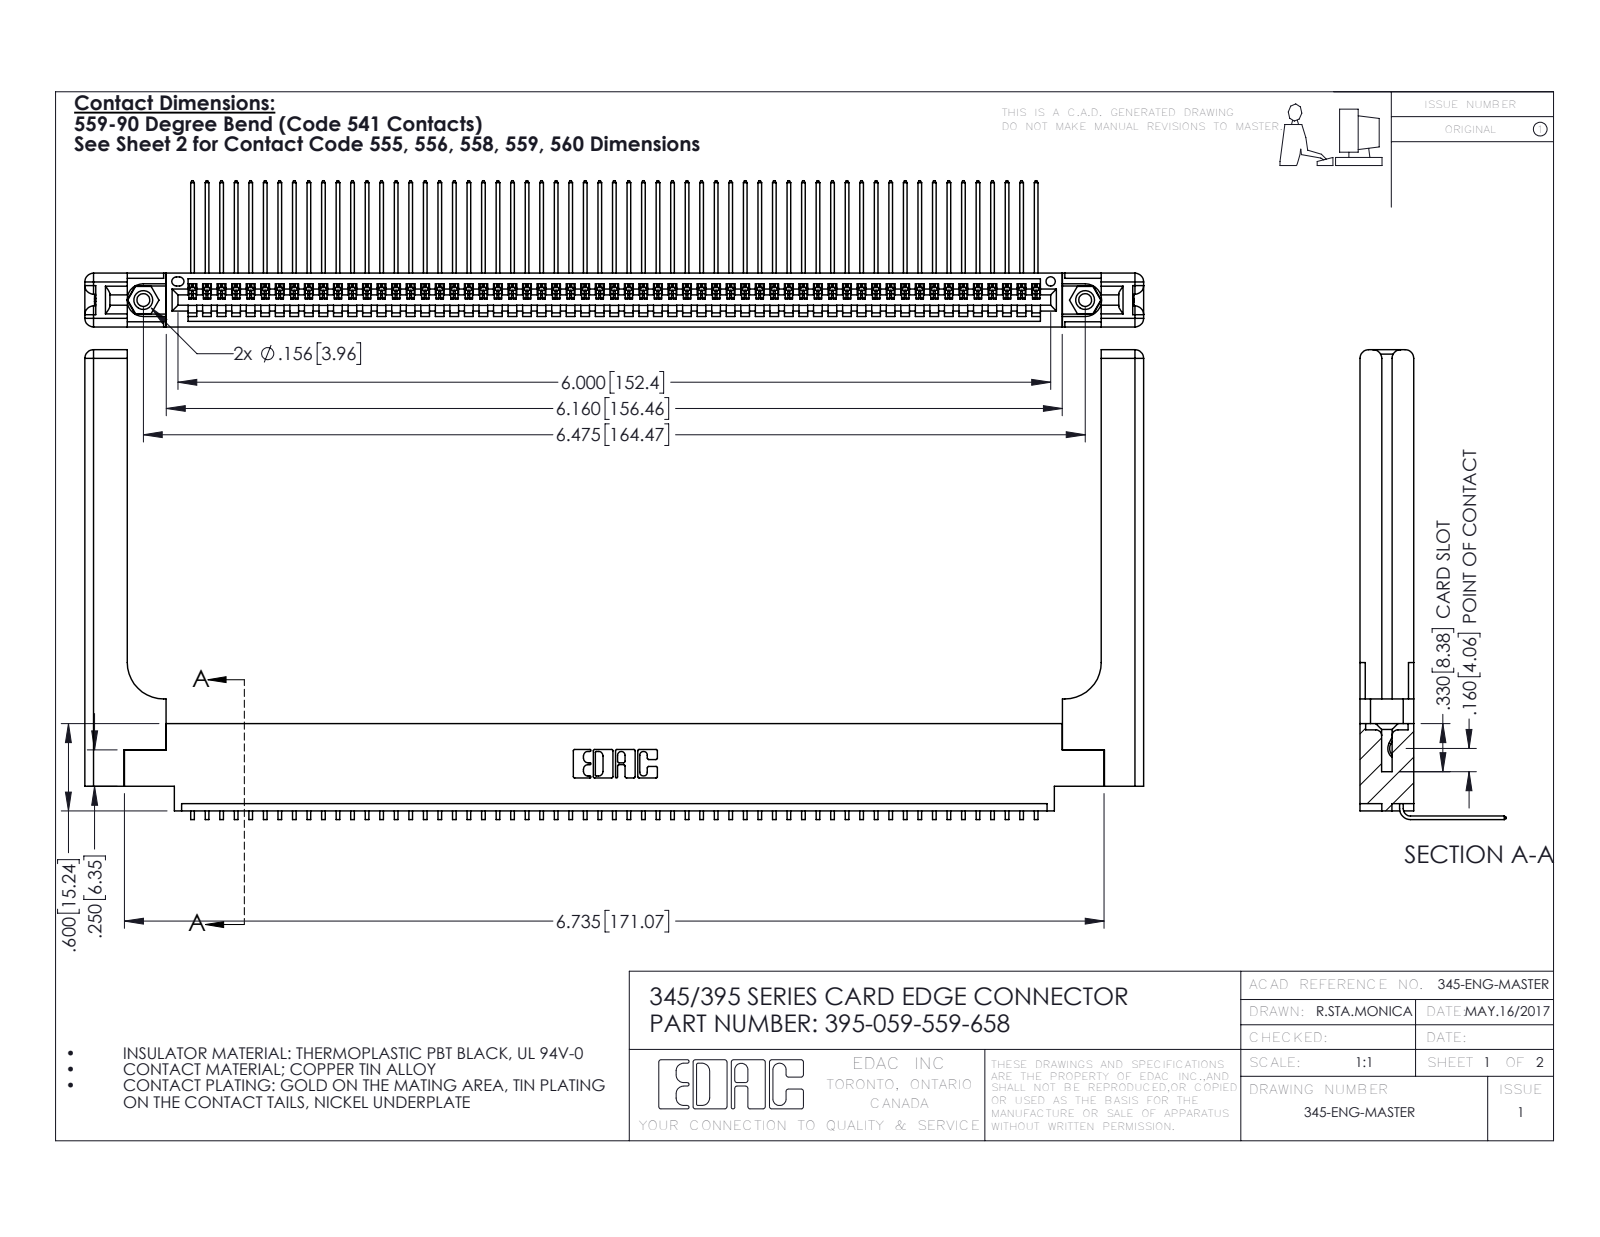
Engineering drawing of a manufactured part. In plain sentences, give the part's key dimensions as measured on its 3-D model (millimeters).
The part is named "345-220-058_345-220-058; 395-059-559-658; 345-292-001_558 559 Tail - 1; 345-250-001_345-250-001-102 (+1 more)". Its 3-D file was written by "SolidWorks 2016 (CONFIG_CONTROL_DESIGN)". It is 64 solids with 3926 faces: 2710 planar, 1156 cylindrical and 60 other. Overall it measures 184.9 by 82 by 25.5 millimeters. Its volume is 26 280 cubic millimeters and its surface area 30 450 square millimeters. Round holes: 2 of diameter 2.3, 2 of diameter 3.2, 2 of diameter 4, 1 of diameter 1.6. Round bosses or shafts: 2 of diameter 3.9. Partial cylindrical surfaces (rounded edges, fillets, slot ends): 118 of radius 0.2, 22 of radius 0.3, 16 of radius 1.5, 6 of radius 0.2, 6 of radius 0.8, 3 of radius 0.7, 2 of radius 0.8, 2 of radius 0.8. The main face-to-face distances are 9.4, 1.8, 7.6, 2.5, 6.9, 0.6, 5.1, 5.7, 3.8, 3.8. The hole center spacings are 6.9, 158.5, 164.5.
